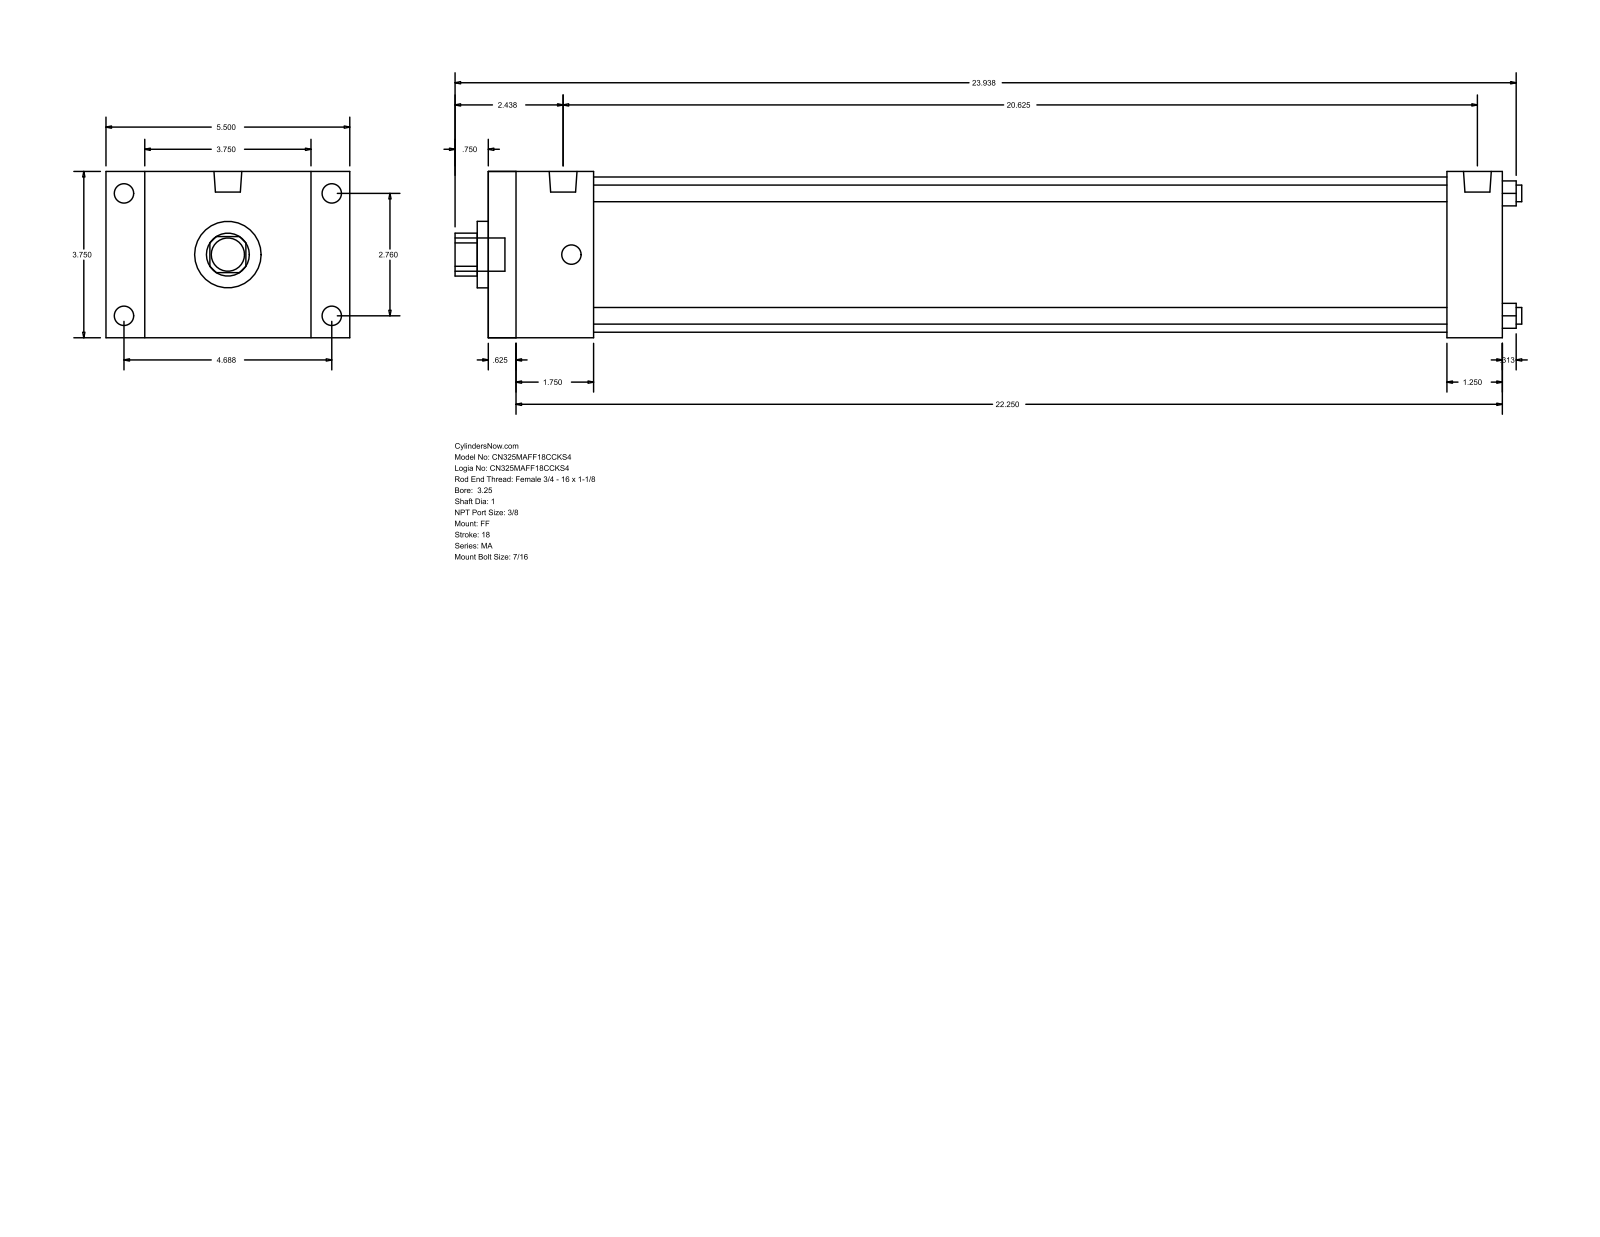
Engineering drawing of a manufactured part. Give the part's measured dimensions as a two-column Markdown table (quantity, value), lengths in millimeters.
| quantity | value |
| --- | --- |
| part name | MA_FF__0325_1 |
| STEP written by | GSSL Pune (CONFIG_CONTROL_DESIGN) |
| units | millimeters |
| bodies | 0 solids, 92 faces (64 planar, 28 cylindrical, 0 other) |
| overall size | 611.19 × 139.7 × 95.25 |
| round holes (diameter × count) | 9.53 × 4, 25.4 × 1, 38.1 × 1, 88.9 × 1 |
| round bosses / shafts (diameter × count) | 11.11 × 8, 15.93 × 2, 19.05 × 1 |
| partial cylindrical surfaces (radius × count) | 12.29 × 1 |
| main face-to-face distances | 95.24, 581.03, 15.87, 565.16, 22.23, 117.47, 60.33, 549.28, 44.46, 533.41 |
| hole center spacings | 49.57, 70.1, 99.14 |
